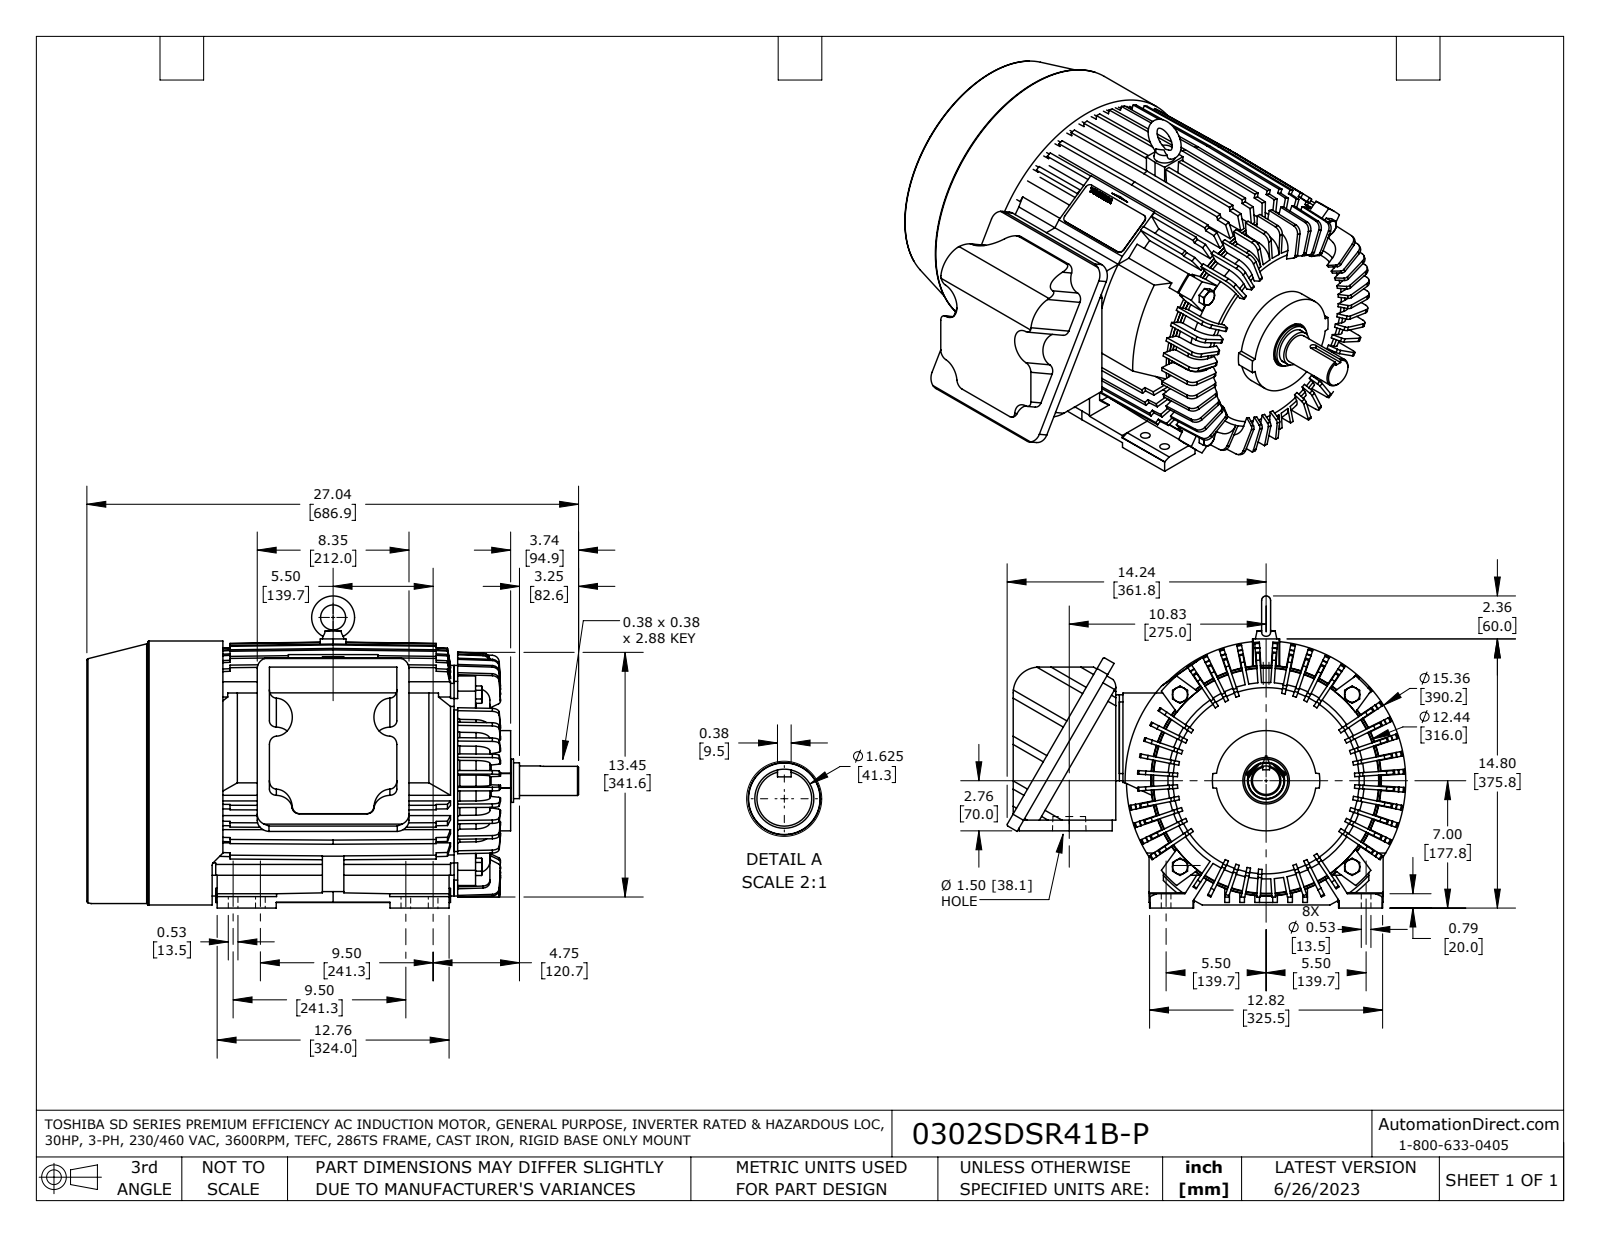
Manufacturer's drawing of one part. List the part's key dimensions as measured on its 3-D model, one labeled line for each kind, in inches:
Part name (STEP PRODUCT): MDSLV002-05-2P-F1-Bottom nc bod broke rep1
STEP written by: SolidWorks 2021 (AUTOMOTIVE_DESIGN)
Units: inches
Bodies: 13 solids, 3158 faces (2342 planar, 250 cylindrical, 566 other)
Overall size (bounding box): 27.043 × 21.924 × 17.157
Volume: 4 040 in³ · Surface area: 4 005 in²
Round holes (diameter × count): ⌀0.354 ×8, ⌀0.531 ×8, ⌀0.087 ×4, ⌀0.398 ×4, ⌀0.551 ×4, ⌀0.472 ×1, ⌀0.545 ×1, ⌀0.827 ×1, ⌀1.988 ×1, ⌀2.559 ×1, ⌀2.661 ×1, ⌀3.937 ×1
Round bosses / shafts (diameter × count): ⌀15.362 ×1, ⌀12.677 ×1, ⌀12.244 ×1, ⌀5.512 ×1, ⌀2.756 ×1, ⌀2.382 ×1, ⌀2.362 ×1, ⌀1.969 ×1
Partial cylindrical surfaces — rounded edges, fillets, slot ends (radius × count): R0.394 ×26, R0.021 ×6, R0.042 ×6, R0.055 ×6, R0.906 ×6, R0.02 ×4, R0.09 ×4, R0.25 ×4
Main face-to-face distances: 0.591, 13.307, 12.717, 0.256, 13.031, 12.441, 0.276, 0.255, 6.89, 0.197
Hole centre spacings: 9.124, 11, 0.492, 1.5, 2.363, 3.341, 6.201, 6.693
